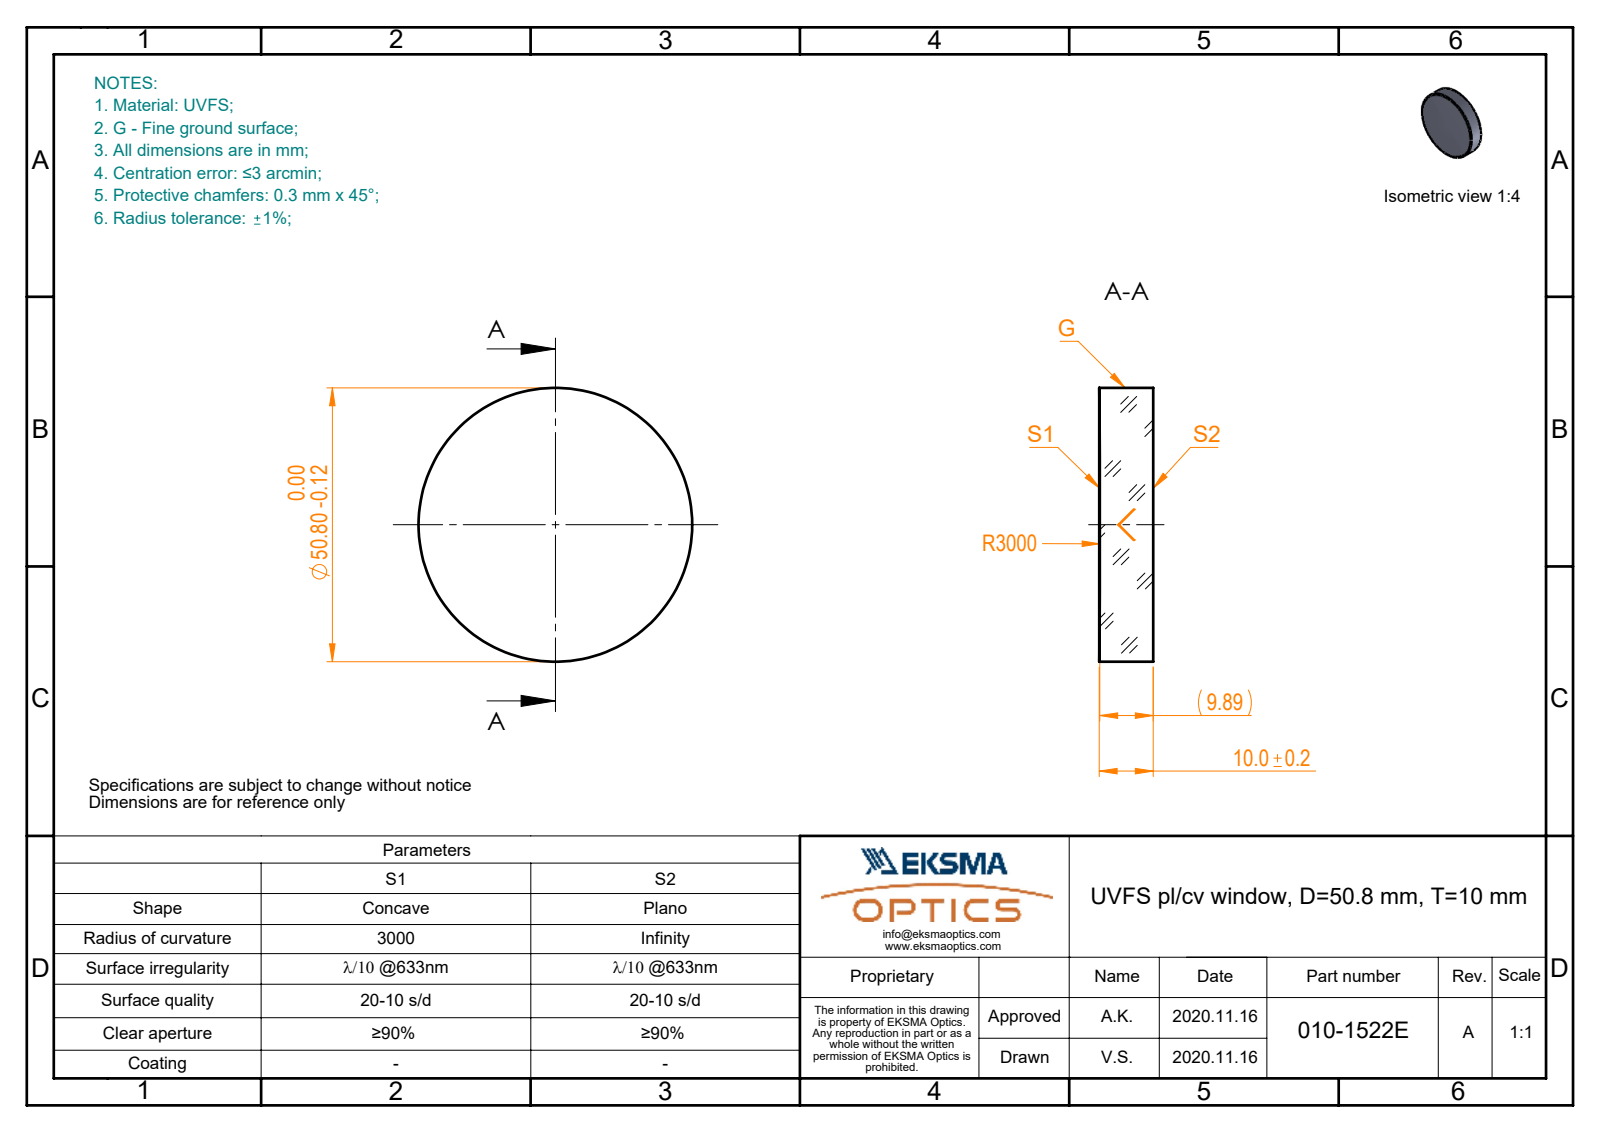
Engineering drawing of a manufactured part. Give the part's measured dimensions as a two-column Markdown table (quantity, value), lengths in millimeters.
| quantity | value |
| --- | --- |
| part name | 010-1522E_UVFS_PCV_window |
| STEP written by | SolidWorks 2019 (CONFIG_CONTROL_DESIGN) |
| units | millimeters |
| bodies | 1 solid, 5 faces (1 planar, 2 cylindrical, 2 other) |
| overall size | 50.8 × 50.8 × 10 |
| volume | 20 159 mm³ |
| surface area | 5 650 mm² |
| round bosses / shafts (diameter × count) | 50.8 × 1 |
